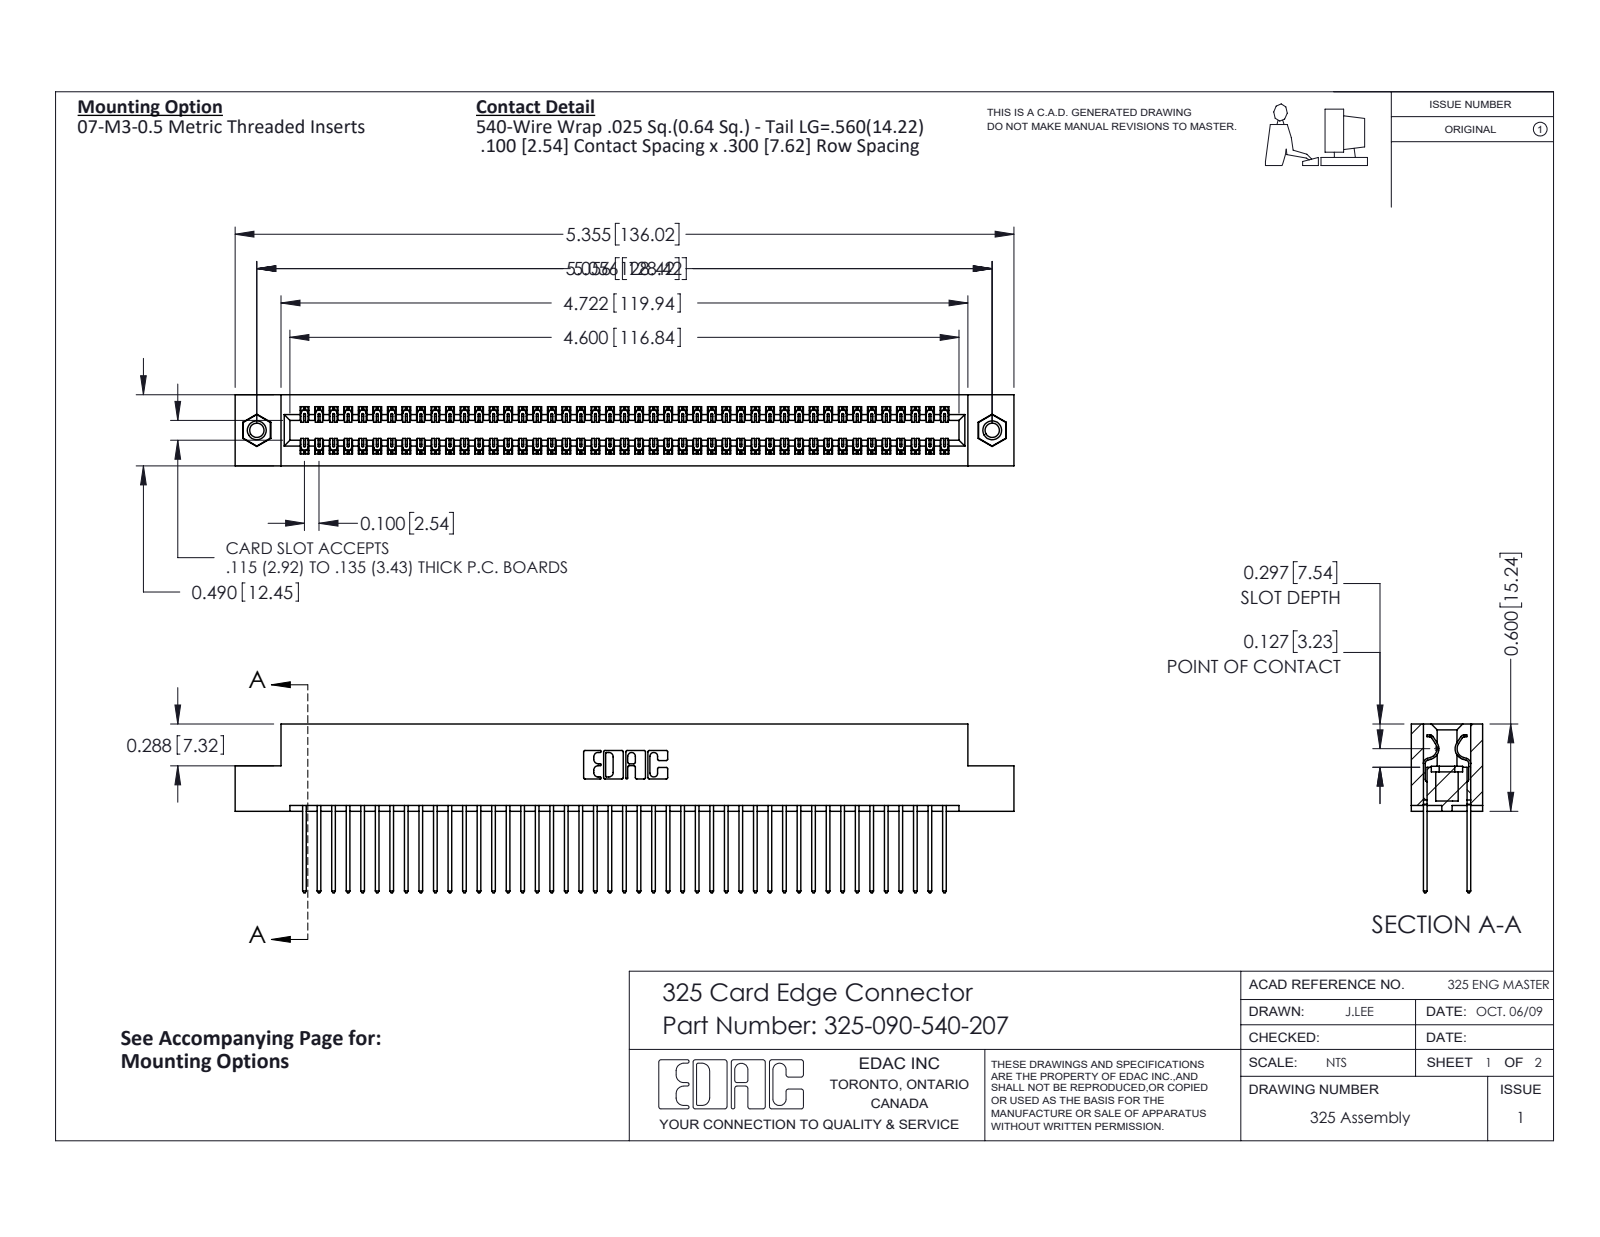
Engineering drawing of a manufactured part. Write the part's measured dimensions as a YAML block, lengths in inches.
part_name: "325-090-540-207; 325 Part_TI; 345-250-001_345-250-005-103; 325-292-001_325-293-140"
step_written_by: "SolidWorks 2016 (CONFIG_CONTROL_DESIGN)"
units: inches
bodies: {solids: 93, faces: 4854, planar: 3342, cylindrical: 1496, other: 16}
overall_size: [5.355, 1.16, 0.49]
volume: 1.093
surface_area: 36.28
round_holes:
  - {diameter: 0.098, count: 2}
  - {diameter: 0.125, count: 2}
  - {diameter: 0.16, count: 2}
round_bosses_or_shafts:
  - {diameter: 0.155, count: 2}
partial_cylinders:
  - {radius: 0.006, count: 135}
  - {radius: 0.01, count: 90}
  - {radius: 0.01, count: 22}
  - {radius: 0.007, count: 6}
  - {radius: 0.031, count: 6}
  - {radius: 0.026, count: 3}
  - {radius: 0.014, count: 2}
  - {radius: 0.022, count: 2}
face_to_face_distances: [0.083, 0.407, 0.3, 0.107, 0.383, 0.025, 0.325, 0.49, 0.275, 0.56]
hole_center_spacings: [5.056]
